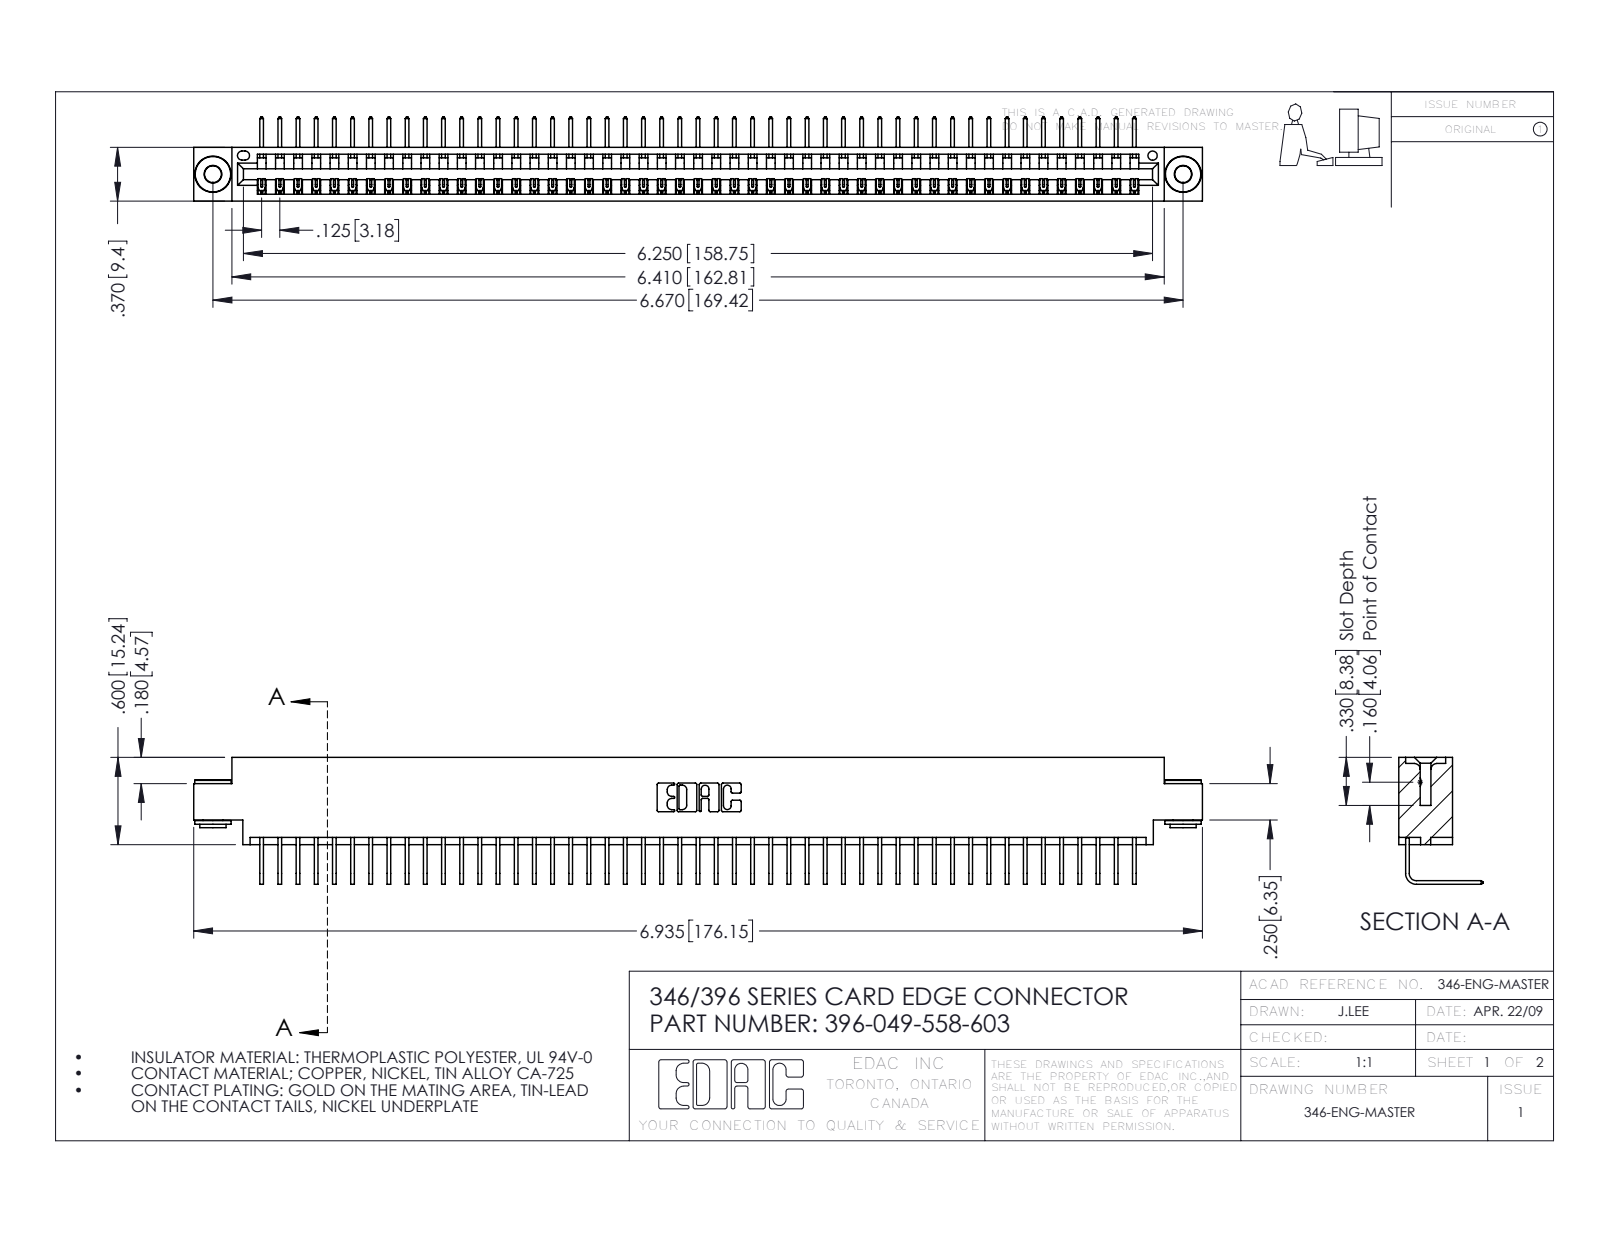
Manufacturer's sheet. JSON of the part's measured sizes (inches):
{"part_name": "345-250-002_345-250-002-102; 346 Part_0.170 Offset - 0.156 Dia-TH; 345-292-001_558 Tail - 2; 396-049-558-603", "step_written_by": "SolidWorks 2016 (CONFIG_CONTROL_DESIGN)", "units": "inches", "bodies": {"solids": 52, "faces": 3104, "planar": 2148, "cylindrical": 948, "other": 8}, "overall_size": [6.935, 0.873, 0.58], "volume_in3": 1.034, "surface_area_in2": 35.03, "round_holes": [[0.116, 2], [0.156, 2], [0.064, 1]], "round_bosses_or_shafts": [[0.25, 2], [0.18, 2], [0.136, 2]], "partial_cylinders_radius": [[0.006, 98], [0.01, 22], [0.007, 6], [0.031, 6], [0.026, 3], [0.031, 2], [0.04, 2], [0.014, 1]], "face_to_face_distances": [0.322, 0.048, 0.37, 0.25, 0.025, 0.298, 0.072, 0.148, 0.222, 0.1], "hole_center_spacings": [0.246, 6.461, 6.67]}
